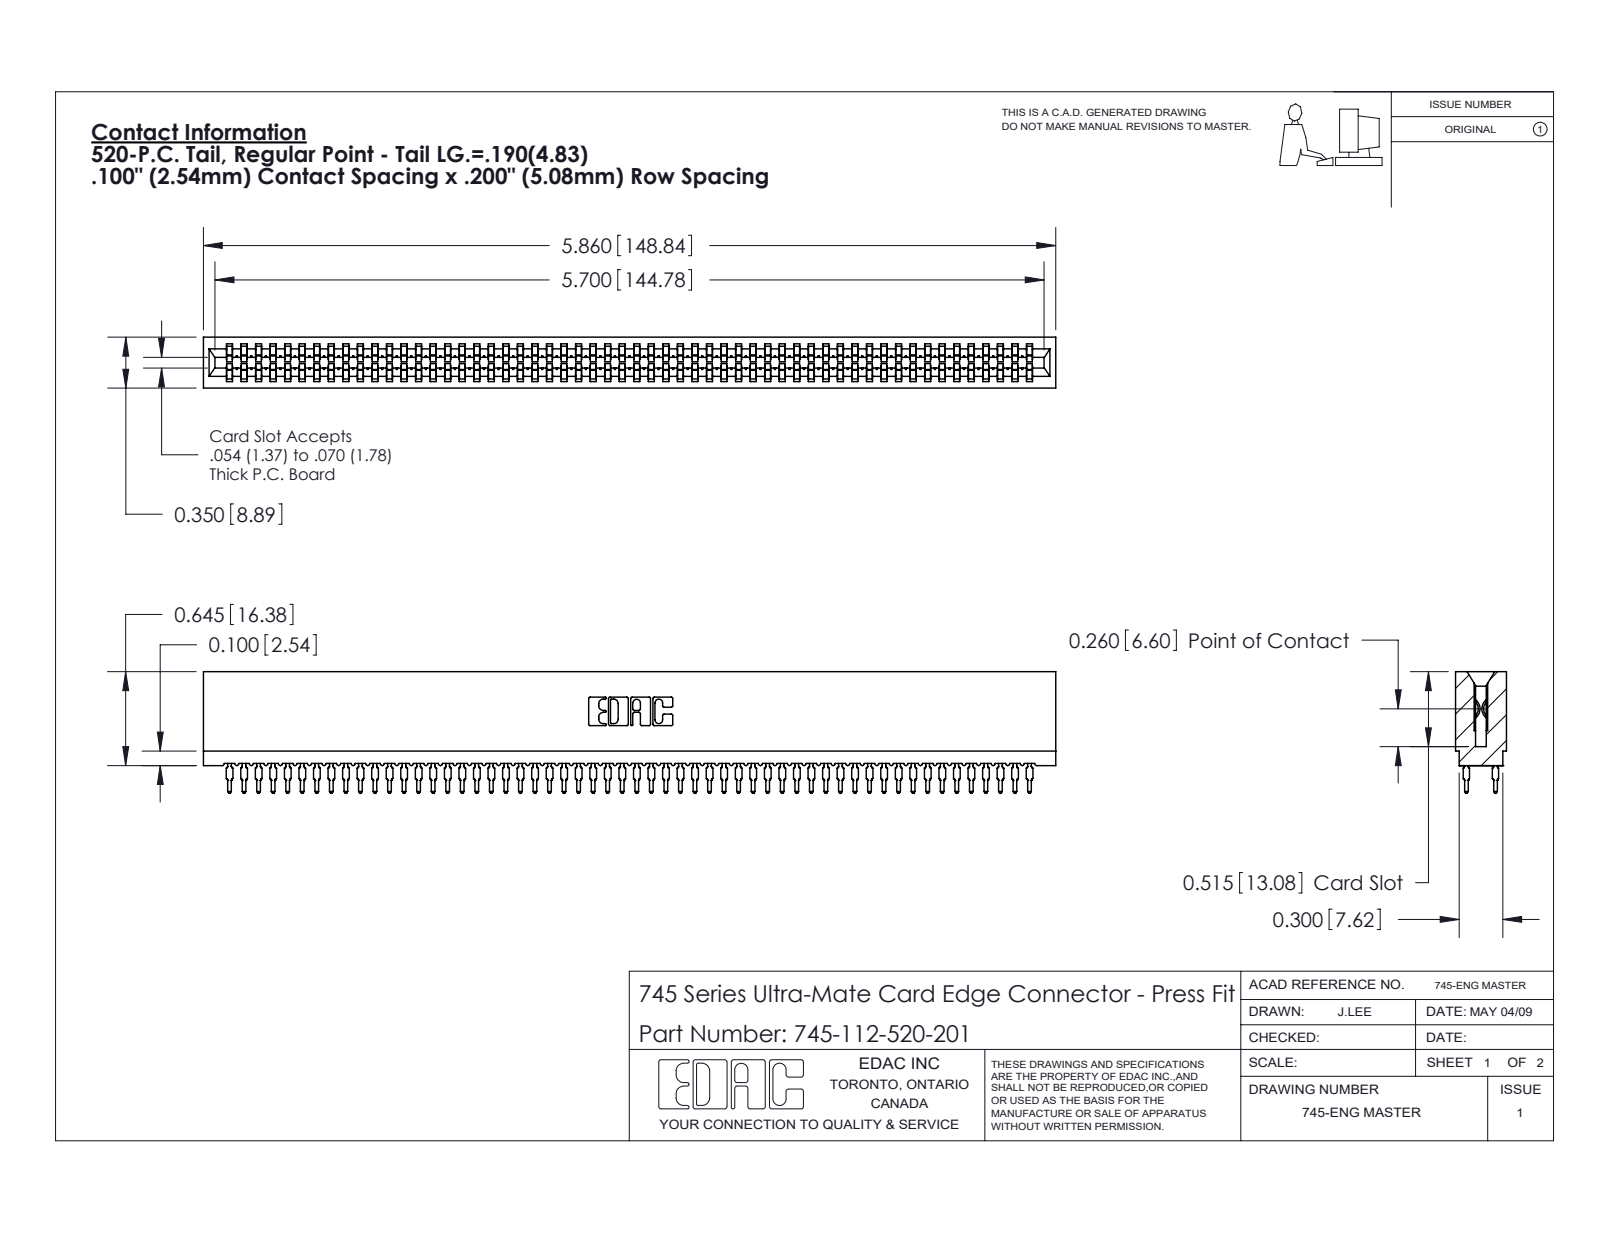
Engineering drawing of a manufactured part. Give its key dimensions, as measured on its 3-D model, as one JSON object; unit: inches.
{"part_name": "745-292-001_520; 745-112-520-201; 745 Part_Insulator Option - 01", "step_written_by": "SolidWorks 2020 (CONFIG_CONTROL_DESIGN)", "units": "inches", "bodies": {"solids": 113, "faces": 10119, "planar": 5207, "cylindrical": 2000, "other": 2912}, "overall_size": [5.86, 0.836, 0.35], "volume_in3": 0.807, "surface_area_in2": 41.38, "partial_cylinders_radius": [[0.021, 224], [0.015, 112], [0.01, 22], [0.005, 8], [0.011, 8], [0.007, 6], [0.031, 6], [0.026, 3]], "face_to_face_distances": [0.35, 0.063, 0.287, 0.045, 0.305, 0.018, 0.243, 0.138, 0.212, 0.093]}
